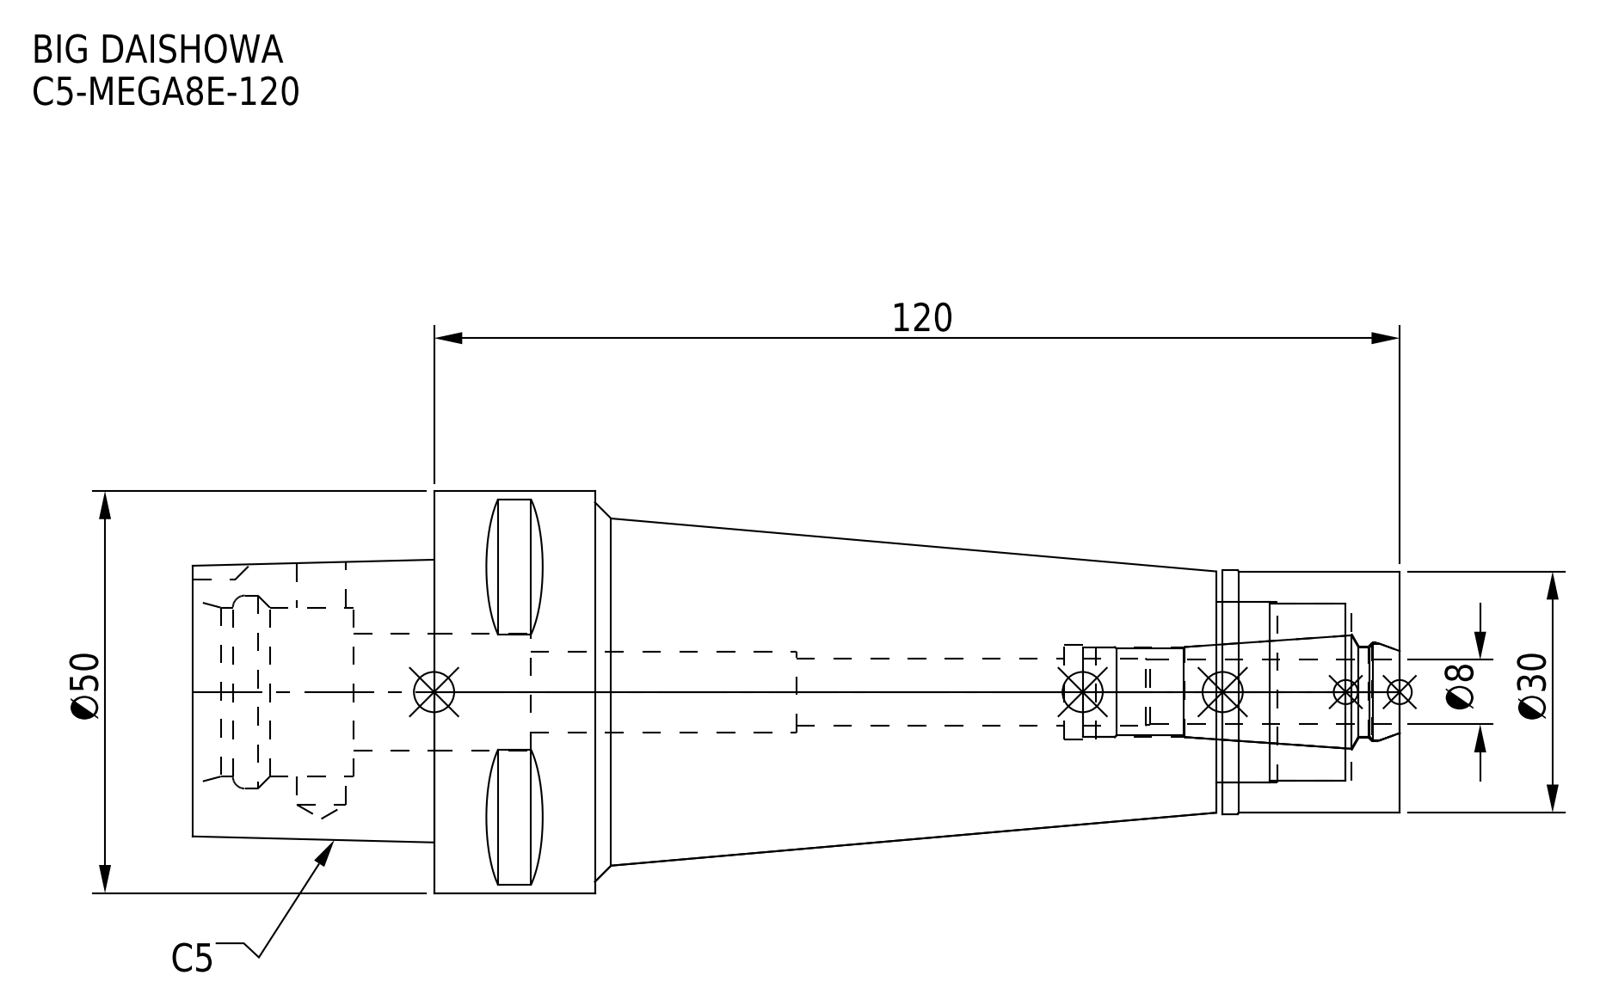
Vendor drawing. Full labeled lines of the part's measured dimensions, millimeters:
Part name (STEP PRODUCT): C5-MEGA8E-120-080.stp; C5-MEGA8E-120_1.stp; C5-MEGA8E-120-080_ASM.stp; MEN8_1.stp (+3 more)
STEP written by: SolidWorks 2019 (CONFIG_CONTROL_DESIGN)
Units: millimetres
Bodies: 2 solids, 100 faces (37 planar, 39 cylindrical, 24 other)
Overall size (bounding box): 150 × 50 × 50
Volume: 144 082 mm³ · Surface area: 29 880 mm²
Round holes (diameter × count): ⌀6.1 ×1, ⌀8.4 ×1, ⌀10 ×1, ⌀11.2 ×1, ⌀11.4 ×1, ⌀11.8 ×1, ⌀12.3 ×1, ⌀14.5 ×1, ⌀21 ×1, ⌀22 ×1, ⌀22.5 ×1, ⌀24 ×1
Round bosses / shafts (diameter × count): ⌀50 ×1, ⌀30.3 ×1, ⌀30 ×1
Partial cylindrical surfaces — rounded edges, fillets, slot ends (radius × count): R4 ×1
Main face-to-face distances: 120, 30, 22, 20, 150, 98, 128, 22.8, 0.8, 97.2
